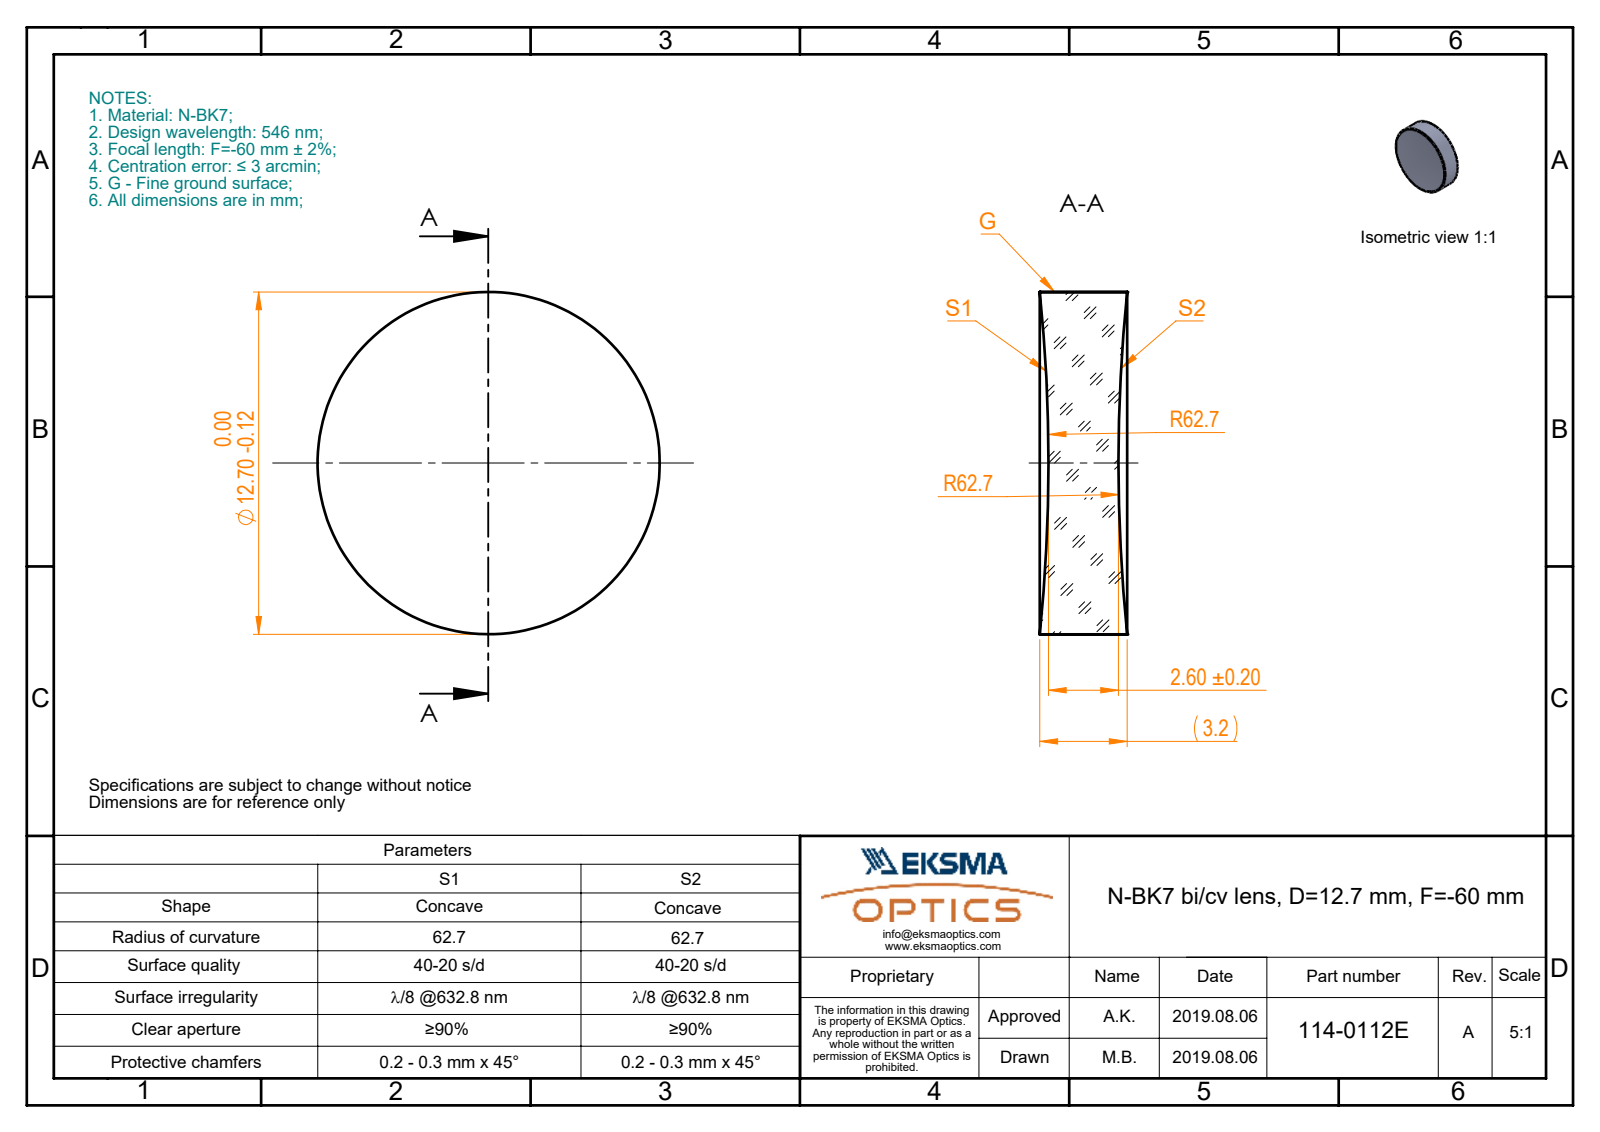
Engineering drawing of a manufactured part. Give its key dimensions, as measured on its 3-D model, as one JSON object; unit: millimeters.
{"part_name": "114-0112E BK7 bi-cv 12.7 F-60", "step_written_by": "SolidWorks 2017 (CONFIG_CONTROL_DESIGN)", "units": "millimeters", "bodies": {"solids": 1, "faces": 6, "planar": 0, "cylindrical": 2, "other": 4}, "overall_size": [12.7, 12.7, 3.25], "volume_mm3": 370, "surface_area_mm2": 383, "round_bosses_or_shafts": [[12.7, 1]]}
